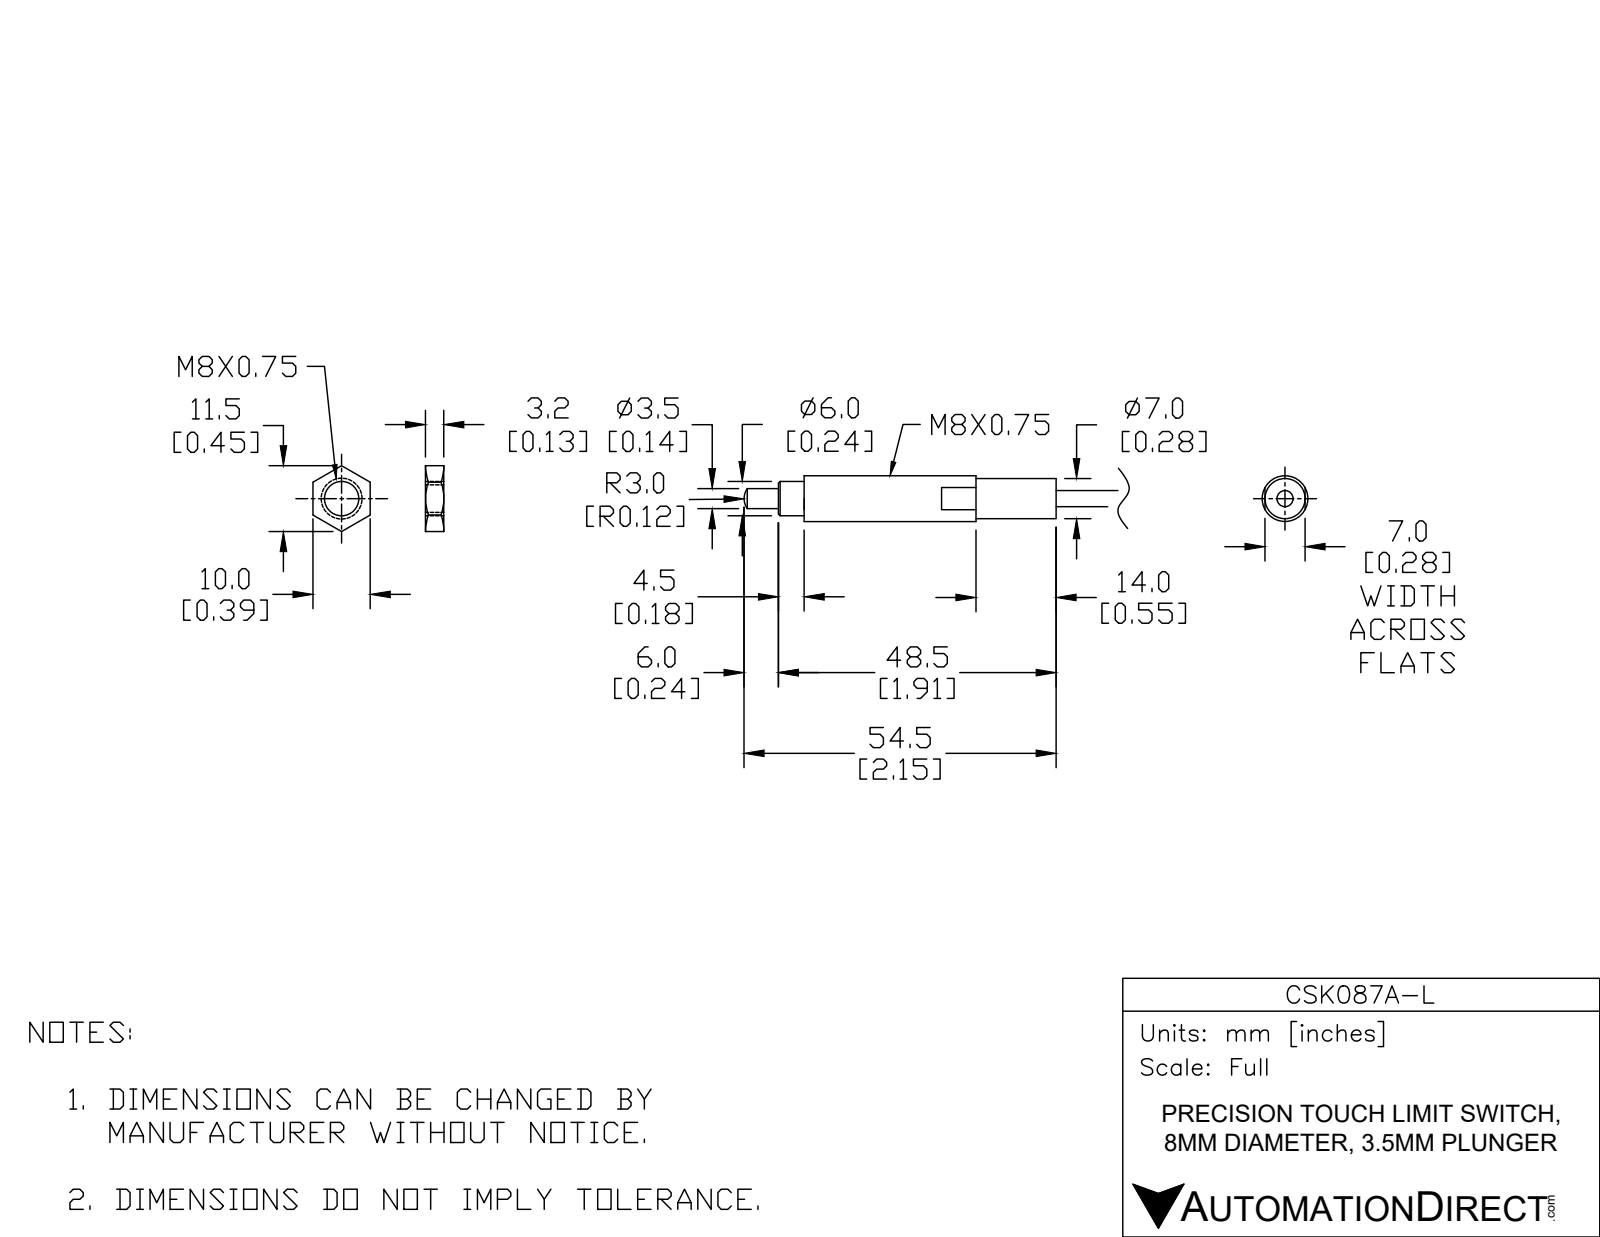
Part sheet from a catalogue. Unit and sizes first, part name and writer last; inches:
Units: inches
Overall size (bounding box): 2.382 × 0.315 × 0.315
Round bosses / shafts (diameter × count): ⌀0.315 ×1, ⌀0.276 ×1, ⌀0.236 ×1, ⌀0.138 ×1, ⌀0.11 ×1
Partial cylindrical surfaces — rounded edges, fillets, slot ends (radius × count): R0.281 ×1
Main face-to-face distances: 1.732, 0.276, 0.177, 1.909, 0.236, 2.146, 1.969, 0.787, 1.358, 1.181
Volume: 0.127 in³ · Surface area: 2.729 in²
Bodies: 1 solid, 153 faces (10 planar, 90 cylindrical, 53 other)
Part name (STEP PRODUCT): CSK087A-L
STEP written by: SolidWorks 2017 (AUTOMOTIVE_DESIGN)
